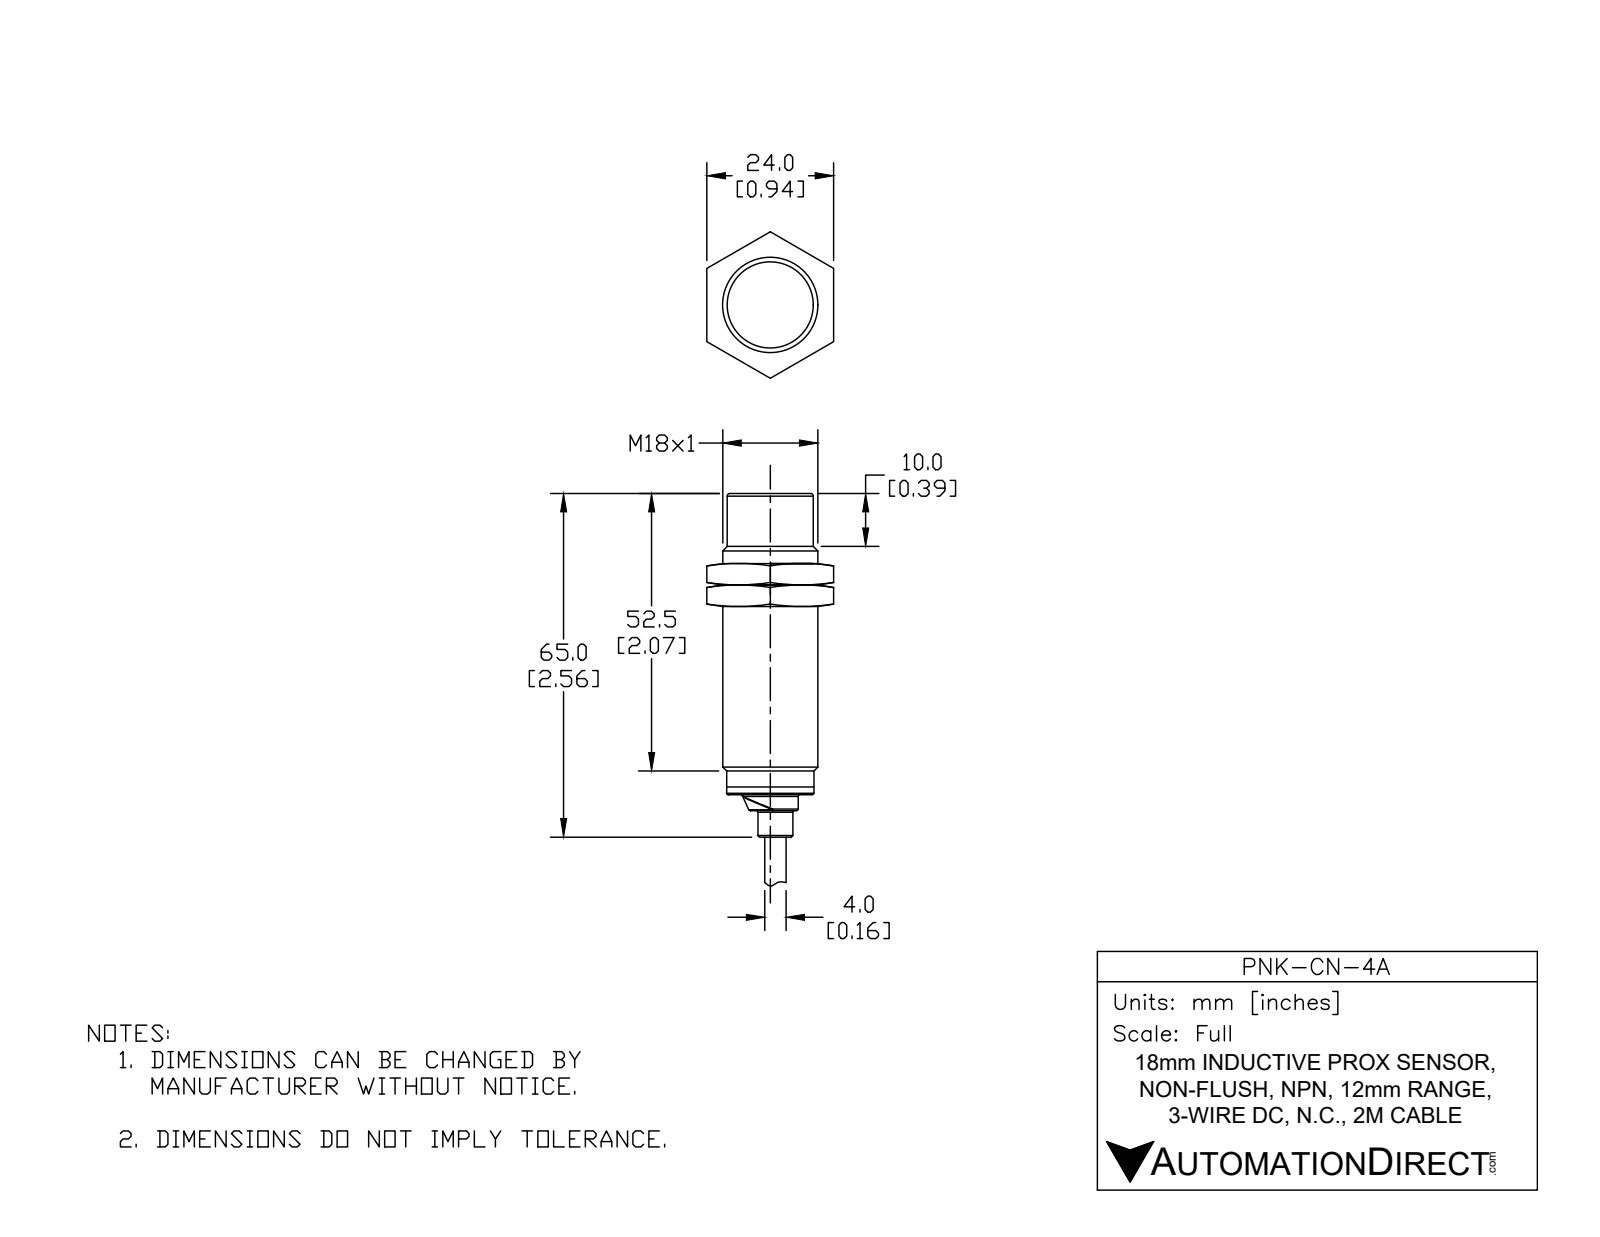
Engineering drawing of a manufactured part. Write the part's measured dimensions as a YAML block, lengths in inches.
part_name: "PNK-CN-4A"
step_written_by: "SolidWorks 2017 (AUTOMOTIVE_DESIGN)"
units: inches
bodies: {solids: 1, faces: 76, planar: 18, cylindrical: 20, other: 38}
overall_size: [4.559, 0.709, 0.709]
volume: 0.936
surface_area: 7.094
round_holes:
  - {diameter: 0.634, count: 1}
round_bosses_or_shafts:
  - {diameter: 0.709, count: 1}
  - {diameter: 0.65, count: 1}
  - {diameter: 0.65, count: 1}
  - {diameter: 0.633, count: 1}
  - {diameter: 0.417, count: 1}
  - {diameter: 0.26, count: 1}
  - {diameter: 0.157, count: 1}
partial_cylinders:
  - {radius: 0.079, count: 1}
  - {radius: 0.081, count: 1}
  - {radius: 0.091, count: 1}
face_to_face_distances: [2.244, 2.362, 0.118, 2.559, 0.315, 0.197, 4.559, 2.315, 2.197, 2]
